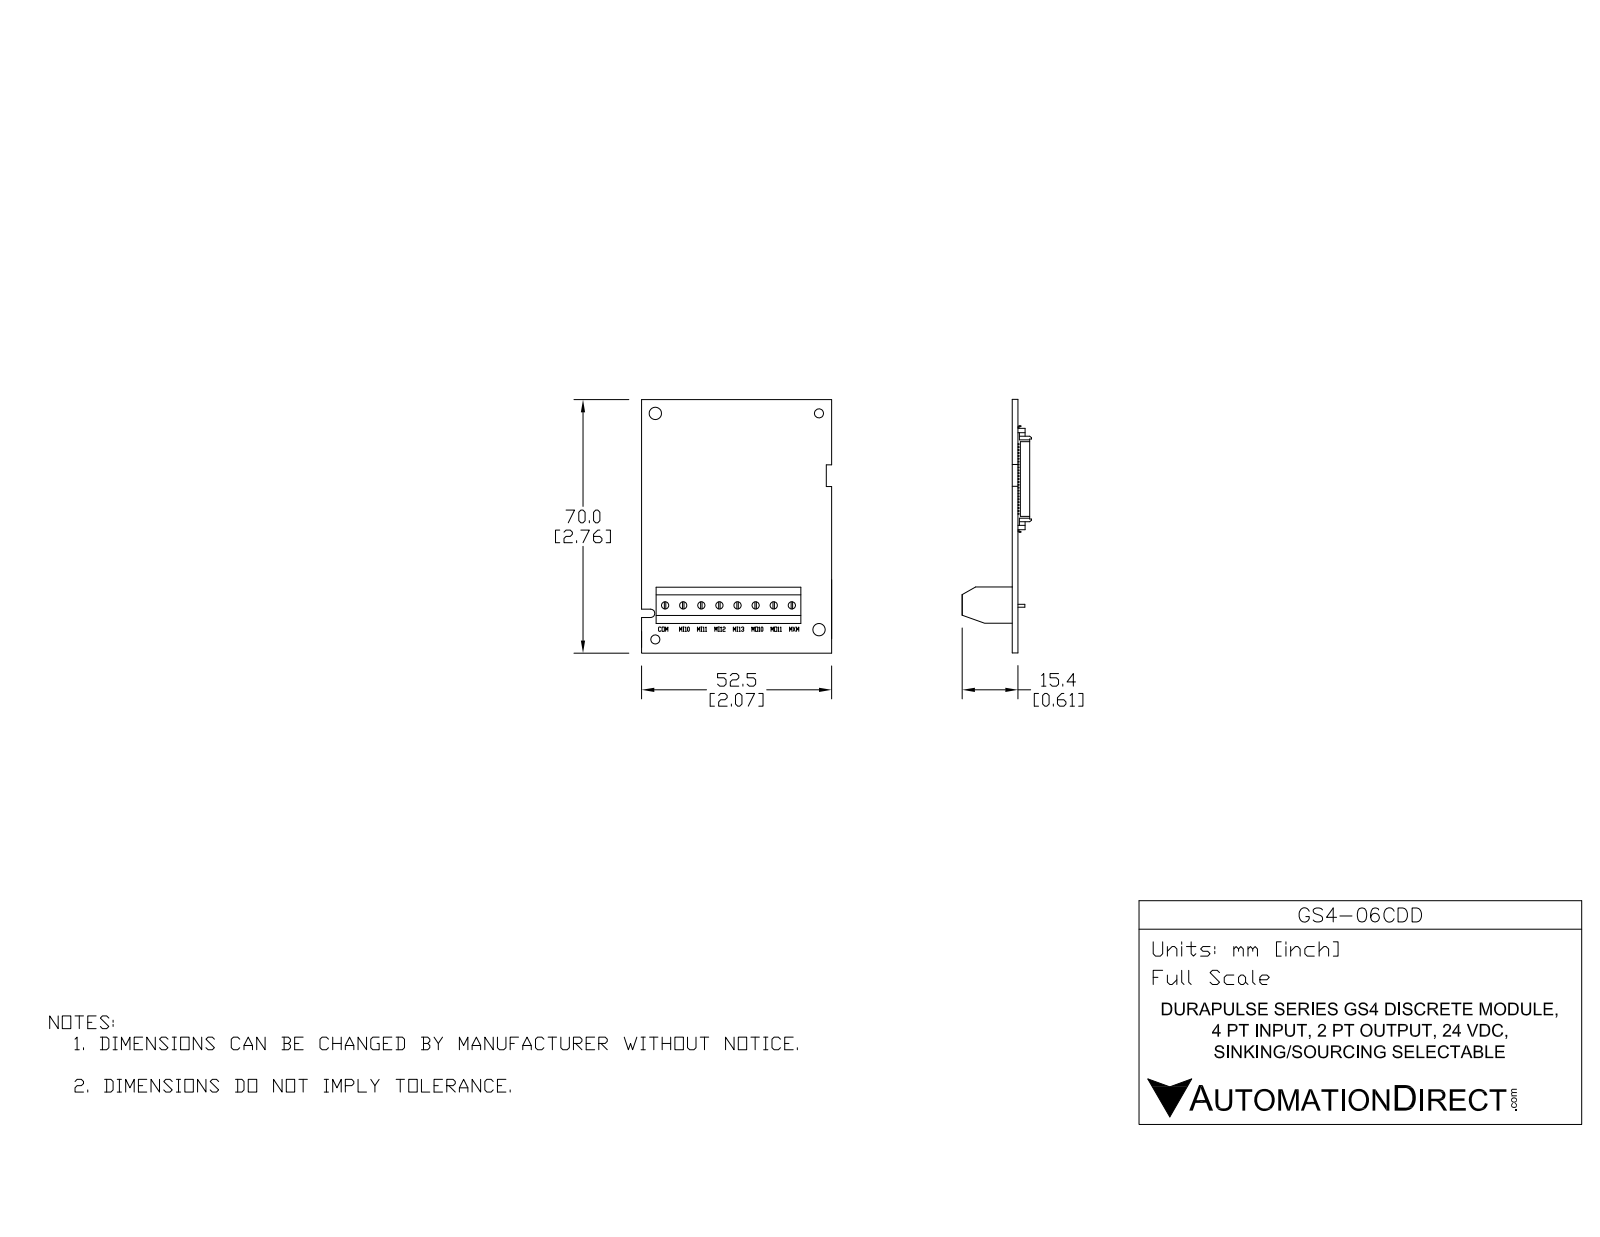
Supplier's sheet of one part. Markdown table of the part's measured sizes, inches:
| quantity | value |
| --- | --- |
| part name | GS4-06CDD |
| STEP written by | SolidWorks 2016 (AUTOMOTIVE_DESIGN) |
| units | inches |
| bodies | 3 solids, 653 faces (588 planar, 61 cylindrical, 4 other) |
| overall size | 2.756 × 2.067 × 0.754 |
| volume | 0.653 in³ |
| surface area | 16.78 in² |
| round holes (diameter × count) | 0.039 × 9, 0.079 × 8, 0.098 × 2, 0.134 × 2, 0.031 × 1 |
| partial cylindrical surfaces (radius × count) | 0.01 × 4, 0.02 × 4, 0.045 × 1 |
| main face-to-face distances | 0.063, 0.079, 0.606, 0.543, 0.394, 0.157, 0.315, 0.02, 1.61, 0.102 |
| hole center spacings | 0.197, 0.394, 0.591, 0.1, 0.787, 0.984, 1.181, 1.42 |
